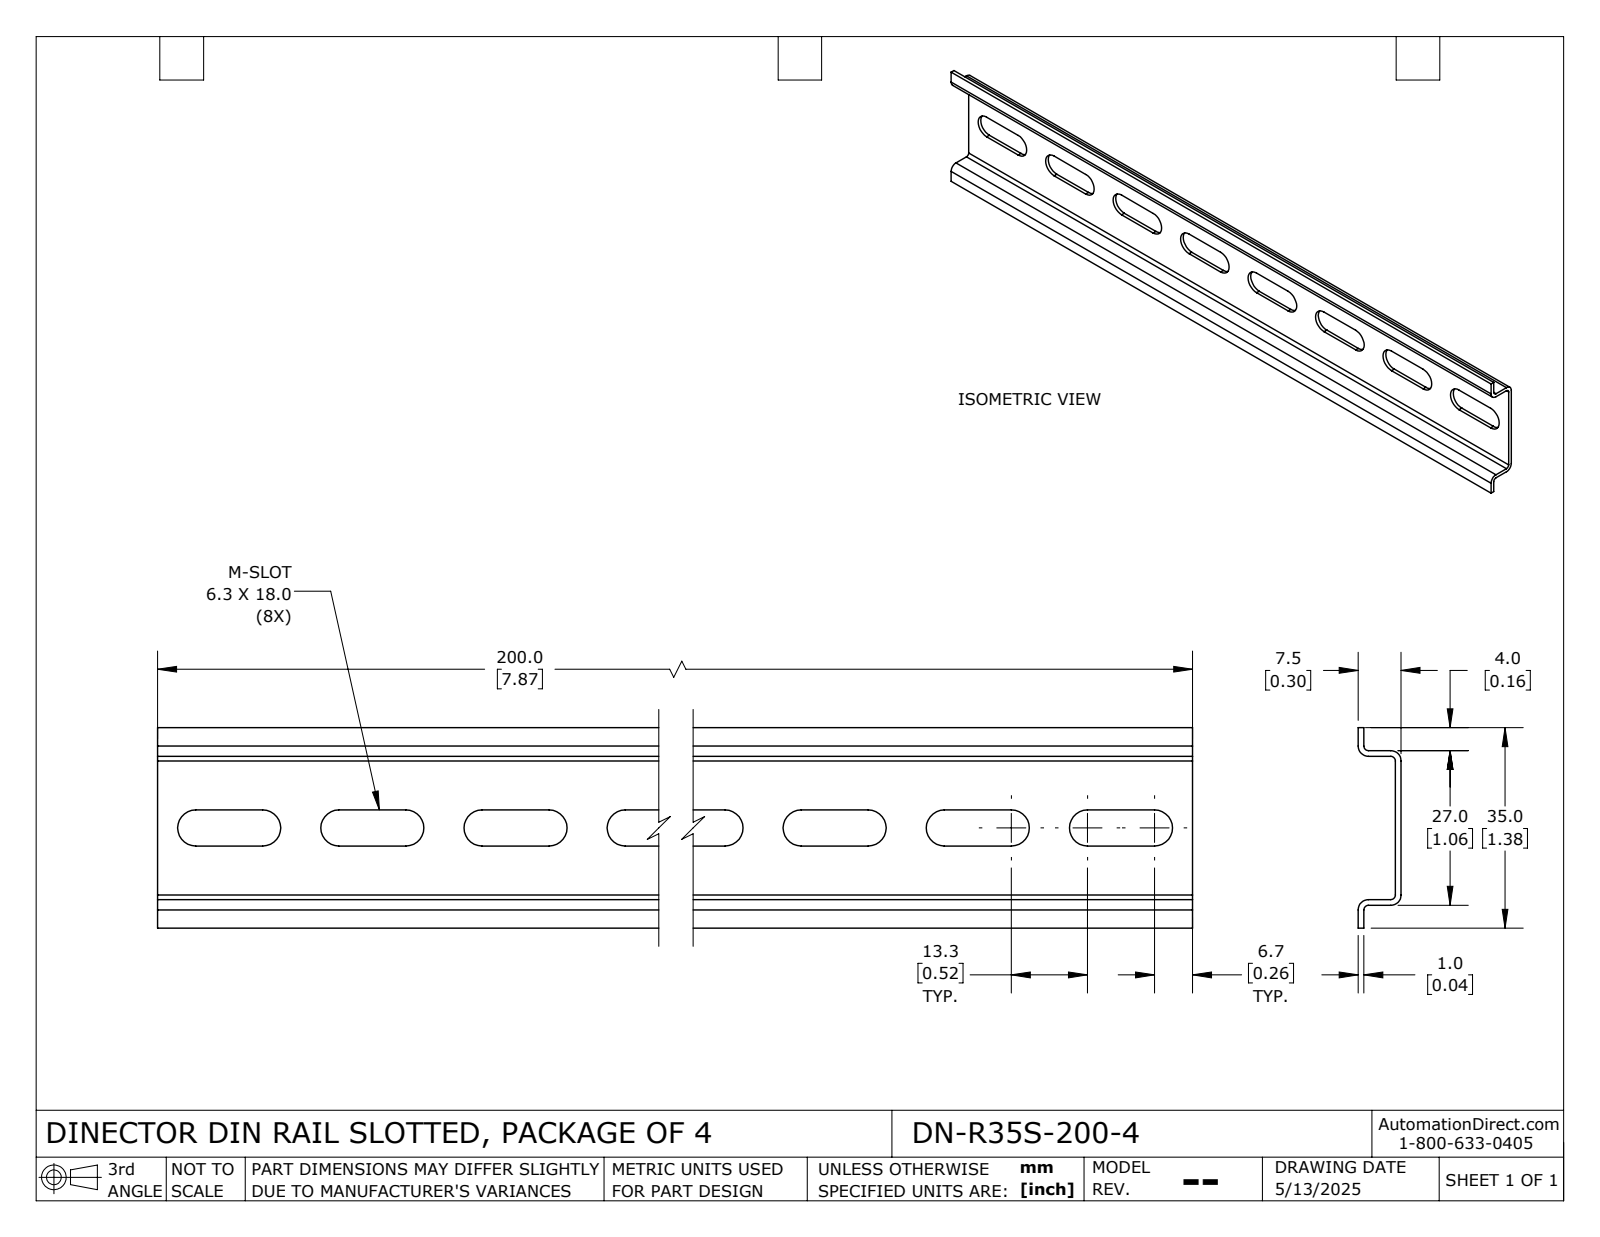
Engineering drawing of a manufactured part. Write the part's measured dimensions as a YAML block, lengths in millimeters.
part_name: "DN-R35S-200-4_Default"
step_written_by: "SolidWorks 2024 (CONFIG_CONTROL_DESIGN)"
units: millimeters
bodies: {solids: 1, faces: 54, planar: 30, cylindrical: 24, other: 0}
overall_size: [200, 35, 7.5]
volume: 8315
surface_area: 17466
partial_cylinders:
  - {radius: 3.15, count: 16}
  - {radius: 0.8, count: 4}
  - {radius: 1.8, count: 4}
face_to_face_distances: [1, 6.5, 26, 7.5, 5.5, 27, 25, 4, 5, 30]
